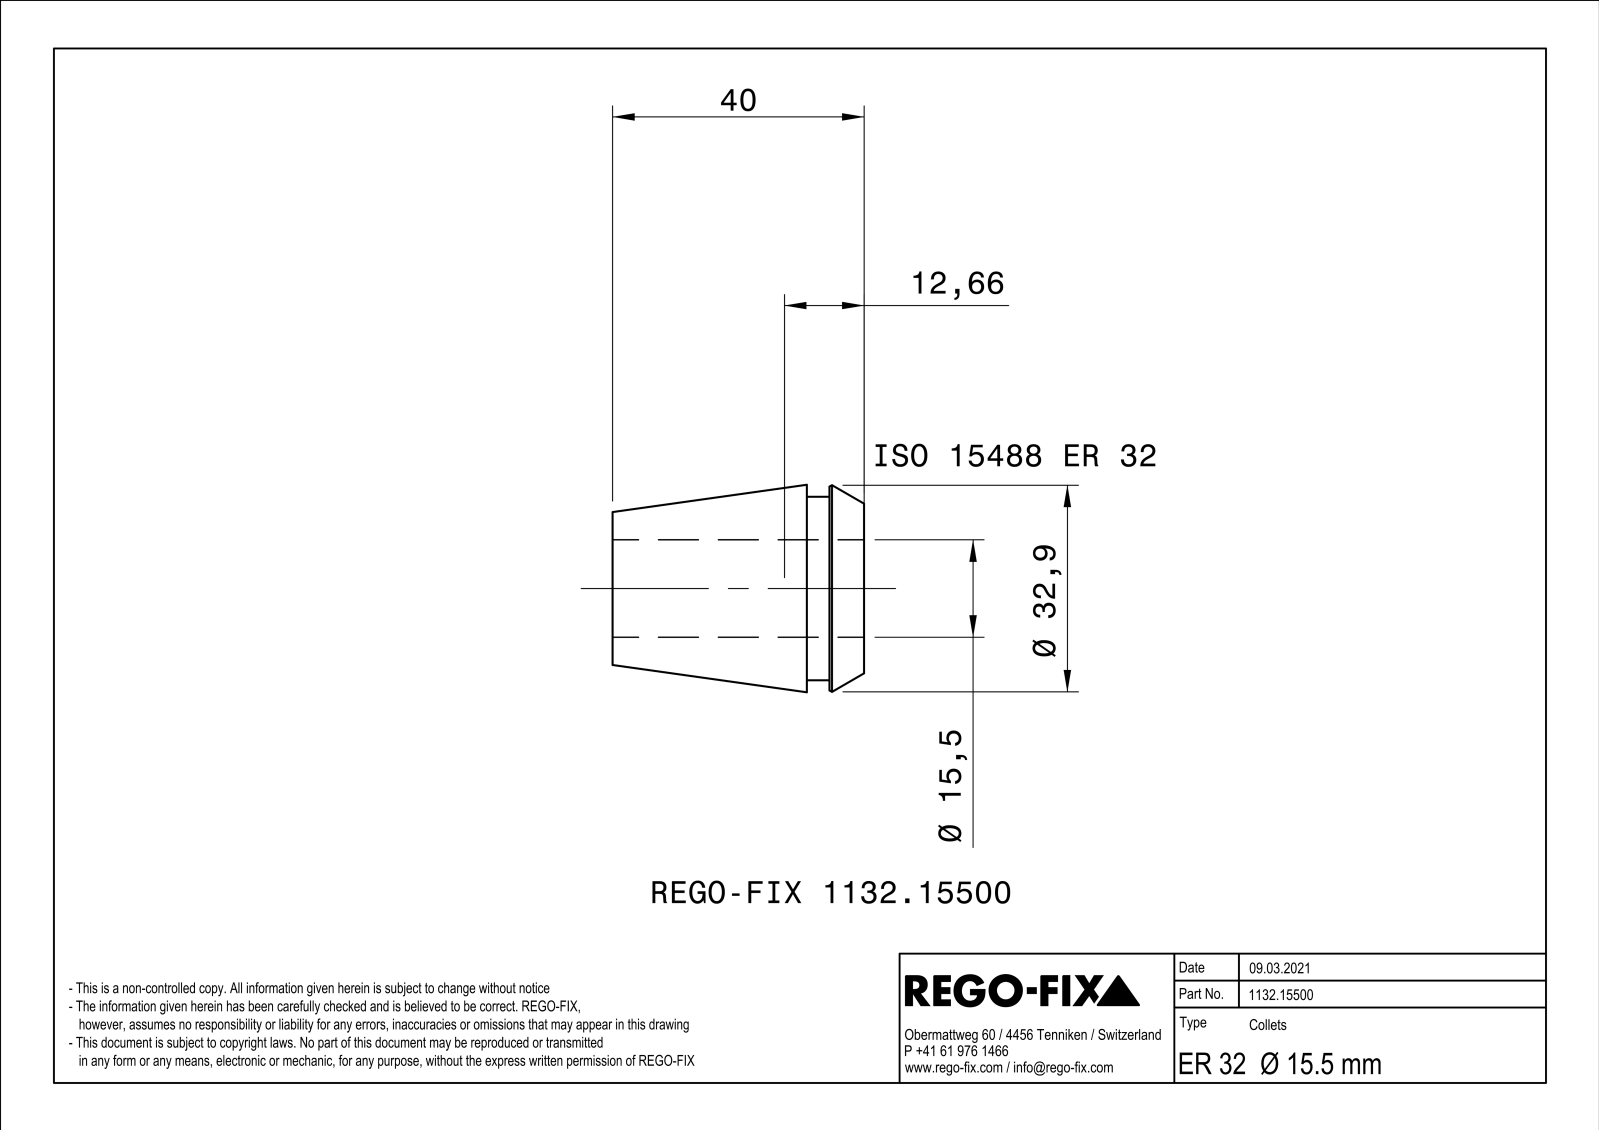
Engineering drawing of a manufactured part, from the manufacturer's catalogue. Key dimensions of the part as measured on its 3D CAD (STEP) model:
Part name (STEP PRODUCT): NOCUT
STEP written by: SIEMENS PLM Software Solid Edge ST10 (AUTOMOTIVE_DESIGN)
Units: millimetres
Bodies: 1 solid, 209 faces (88 planar, 41 cylindrical, 80 other)
Overall size (bounding box): 40 × 32.98 × 32.98
Volume: 15 056 mm³ · Surface area: 13 122 mm²
Round holes (diameter × count): ⌀15.5 ×1
Round bosses / shafts (diameter × count): ⌀29.2 ×1
Partial cylindrical surfaces — rounded edges, fillets, slot ends (radius × count): R0.4 ×20
Main face-to-face distances: 1, 40, 9.1, 30.9, 5.5, 3.6, 34.5, 6, 0.5, 3.1
